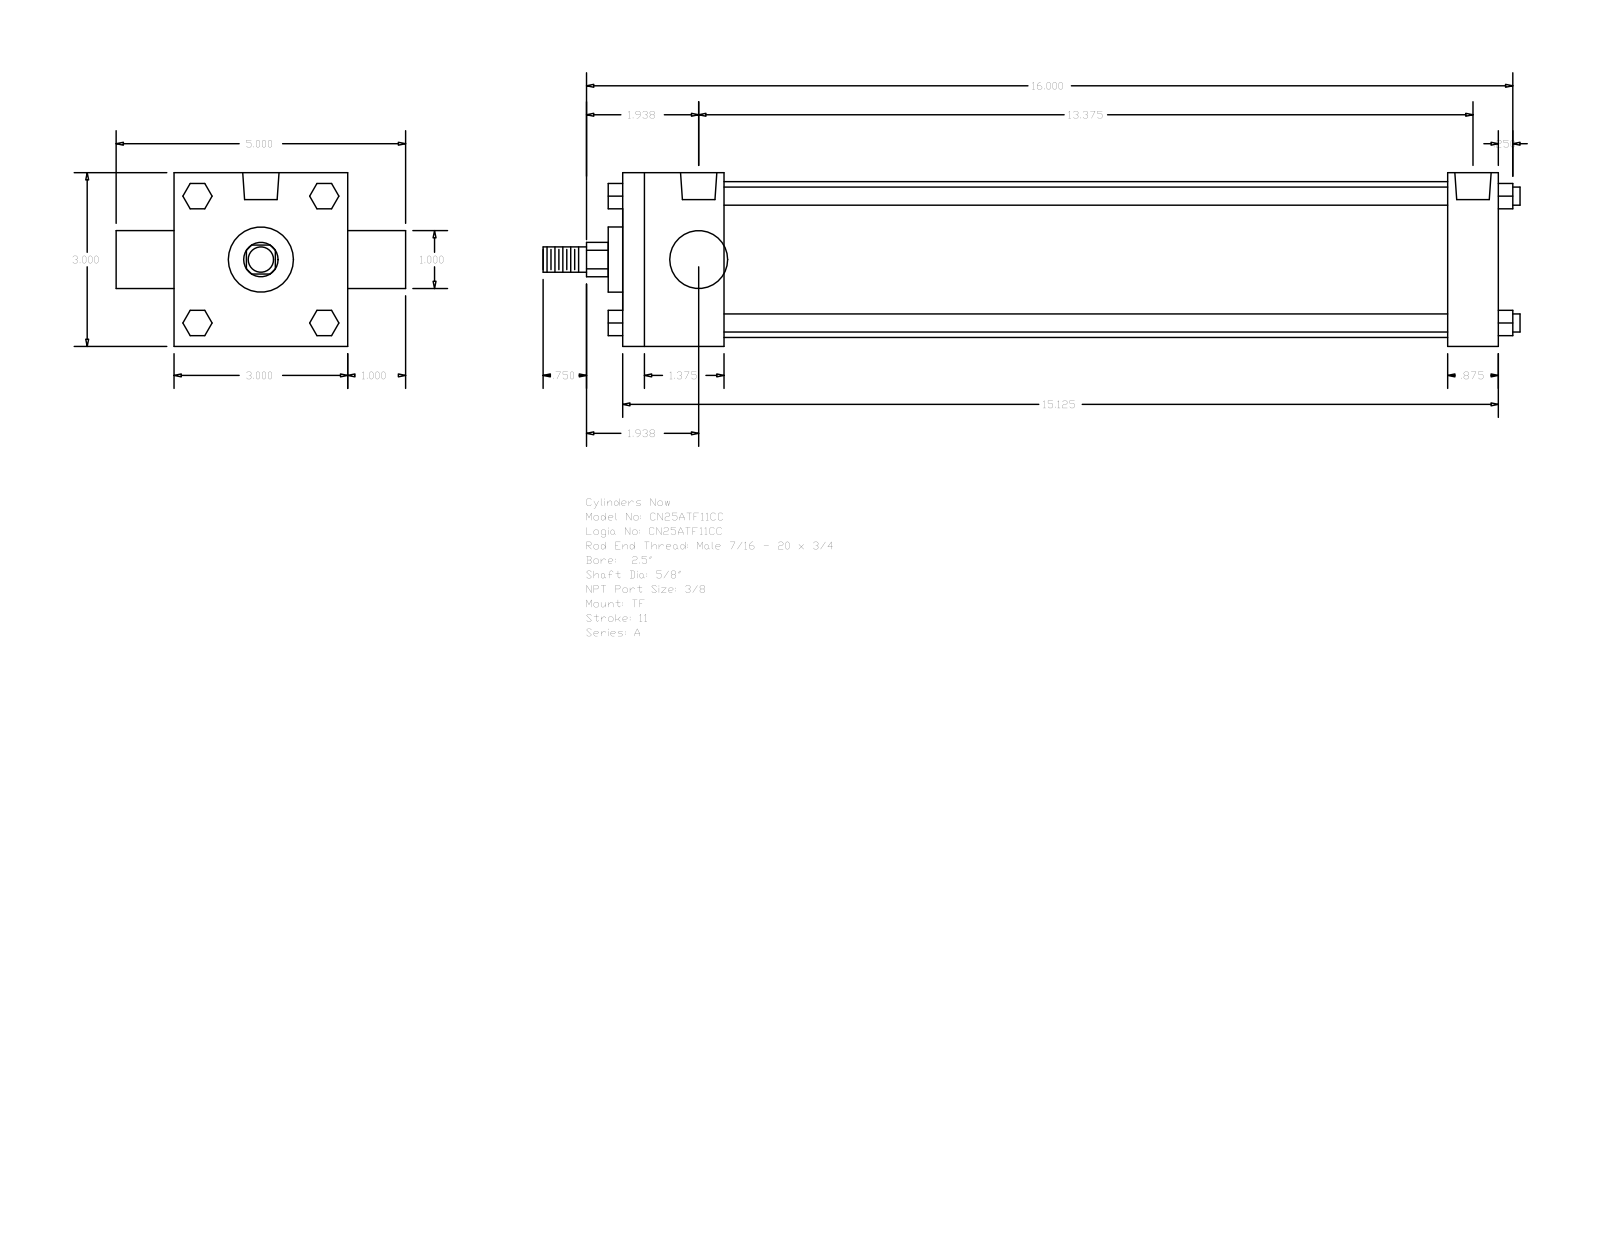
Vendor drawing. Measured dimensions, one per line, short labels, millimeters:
name: A_TF__0250_0.625
written by: GSSL Pune (CONFIG_CONTROL_DESIGN)
unit: mm
bodies: 0 solids, 120 faces (92 planar, 28 cylindrical, 0 other)
size: 428.62 × 127 × 76.2
holes: 3× ⌀5.56, 2× ⌀15.93
bosses: 4× ⌀7.94, 1× ⌀68.33, 1× ⌀28.57, 1× ⌀25.4, 1× ⌀15.88, 1× ⌀11.11
rounds: 1× R7.54
face distances: 76.2, 384.17, 44.45, 361.94, 317.49, 339.72, 22.23, 25.4, 101.6, 6.35
hole spacings: 2.38, 342.11, 339.73, 344.49
